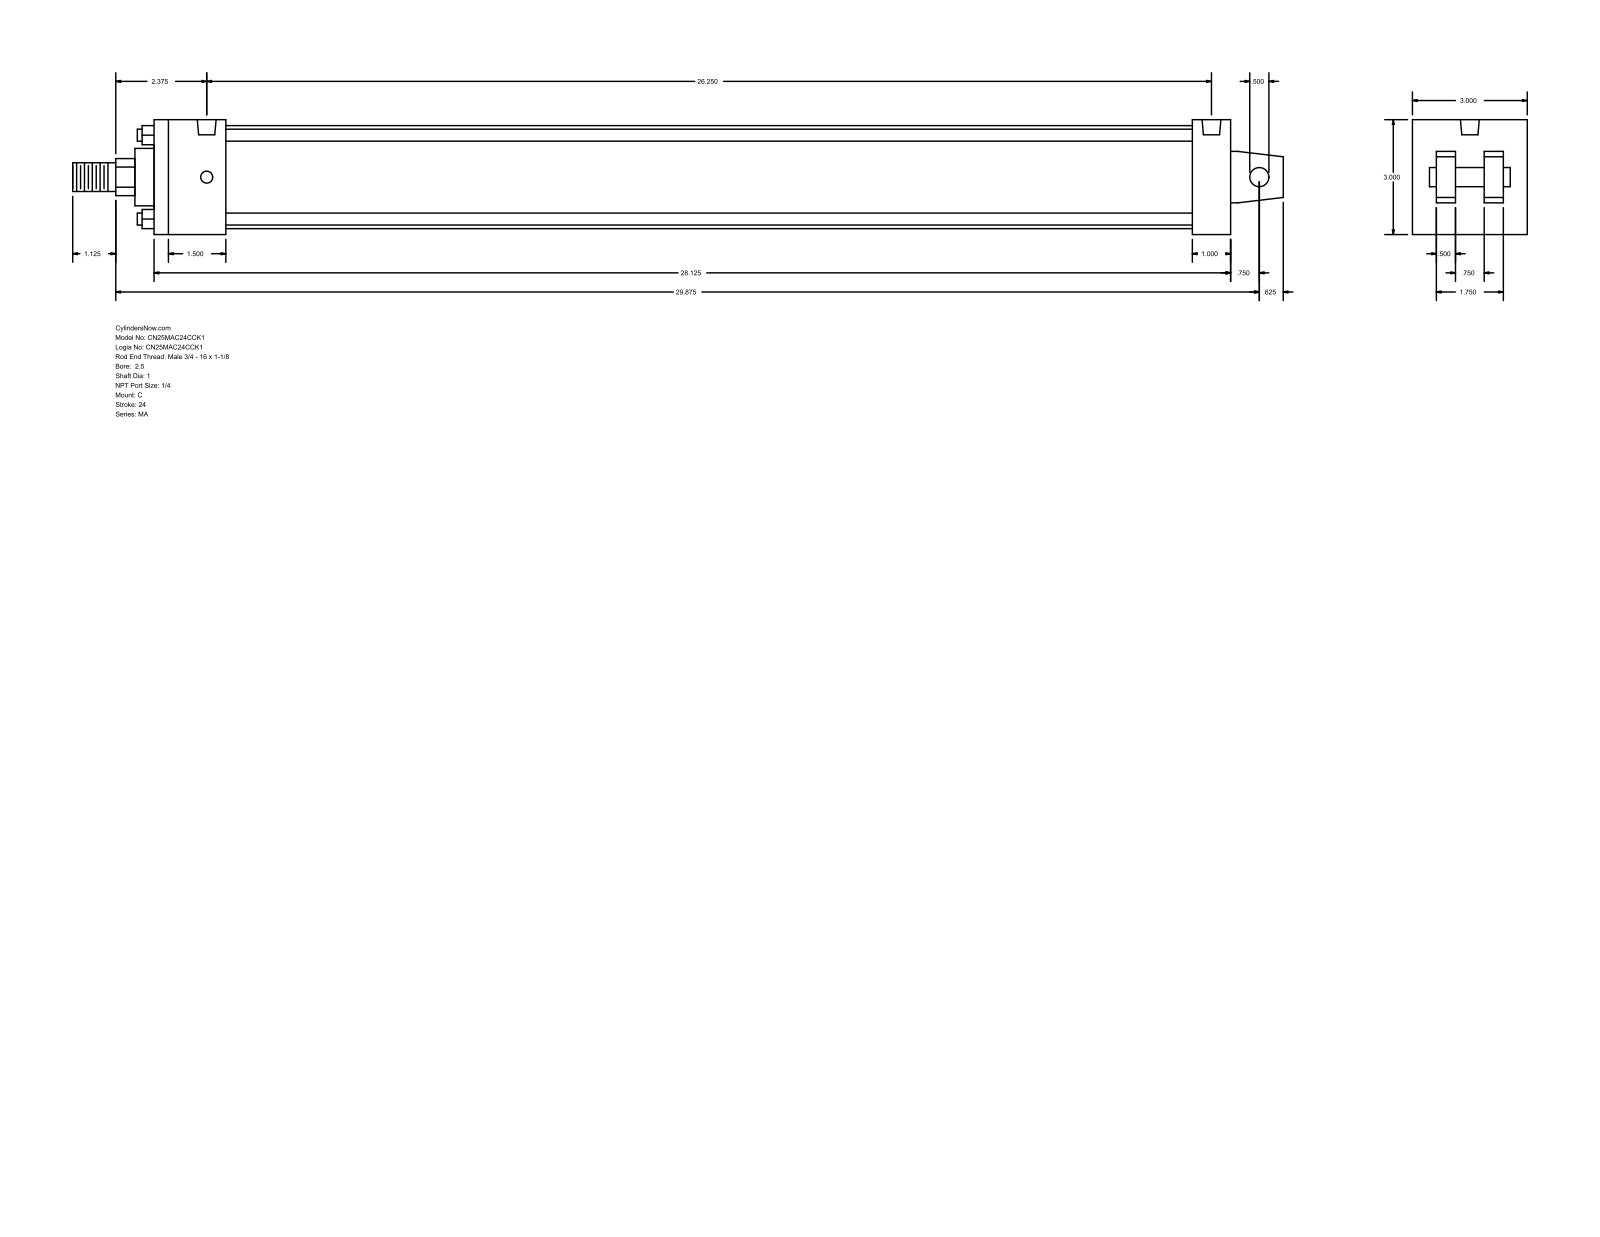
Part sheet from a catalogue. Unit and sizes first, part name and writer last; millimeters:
Units: millimetres
Overall size (bounding box): 803.27 × 76.2 × 76.2
Round holes (diameter × count): ⌀7.94 ×4, ⌀12.49 ×2
Round bosses / shafts (diameter × count): ⌀7.94 ×4, ⌀68.33 ×1, ⌀38.1 ×1, ⌀25.4 ×1, ⌀19.05 ×1, ⌀12.7 ×1
Partial cylindrical surfaces — rounded edges, fillets, slot ends (radius × count): R12.29 ×1
Main face-to-face distances: 76.2, 47.63, 714.37, 12.7, 60.33, 15.87, 28.57, 688.98, 641.35, 666.74
Hole centre spacings: 666.75
Bodies: 0 solids, 103 faces (76 planar, 27 cylindrical, 0 other)
Part name (STEP PRODUCT): MA_C__0250_1
STEP written by: GSSL Pune (CONFIG_CONTROL_DESIGN)
